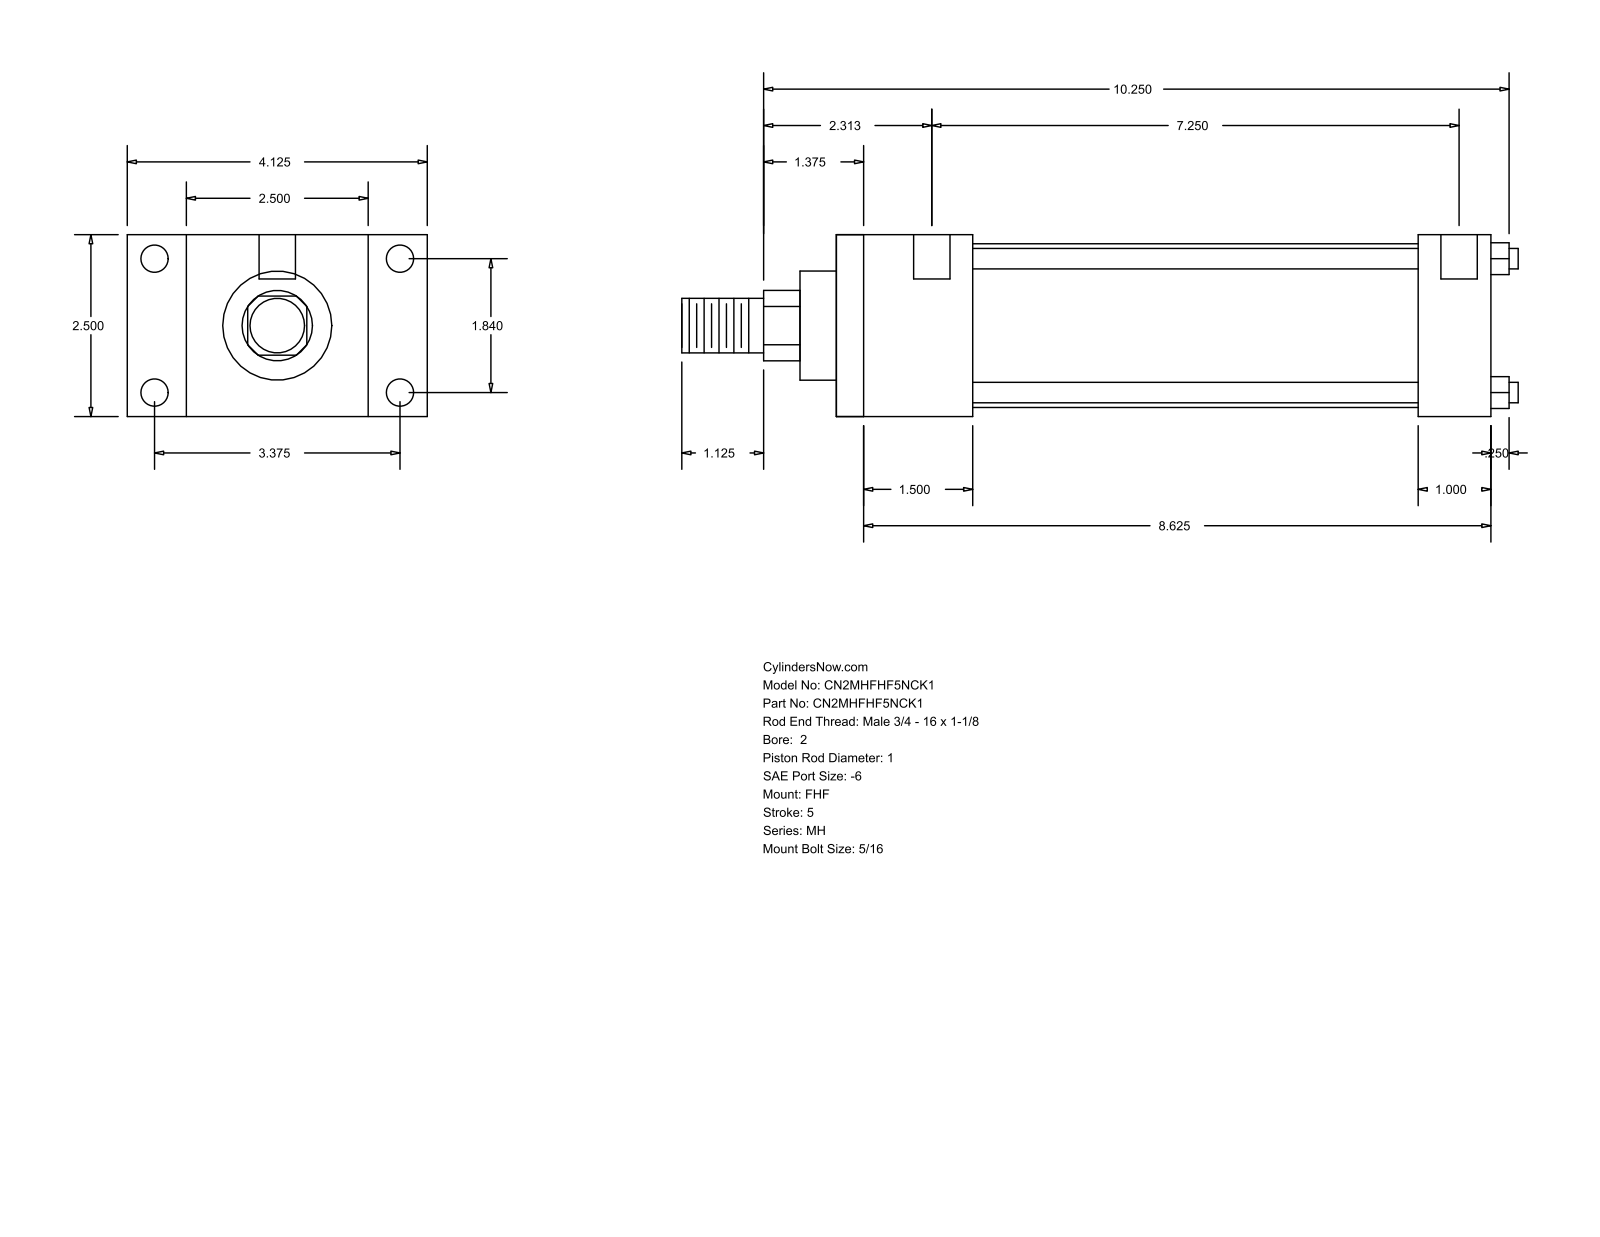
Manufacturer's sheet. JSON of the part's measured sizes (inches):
{"part_name": "MH_FHF__0200_1", "step_written_by": "GSSL Pune (CONFIG_CONTROL_DESIGN)", "units": "inches", "bodies": {"solids": 0, "faces": 88, "planar": 60, "cylindrical": 28, "other": 0}, "overall_size": [11.5, 4.125, 2.5], "round_holes": [[0.219, 4], [0.375, 4], [0.5, 2]], "round_bosses_or_shafts": [[0.281, 4], [2.25, 1], [1.5, 1], [1, 1], [0.75, 1]], "partial_cylinders_radius": [[0.484, 1]], "face_to_face_distances": [2.5, 9, 1.875, 7.125, 0.813, 3.313, 4.125, 1, 8, 6.125], "hole_center_spacings": [1.84, 3.375, 3.844, 7.562, 0.125, 0.187, 7.25, 7.375]}
